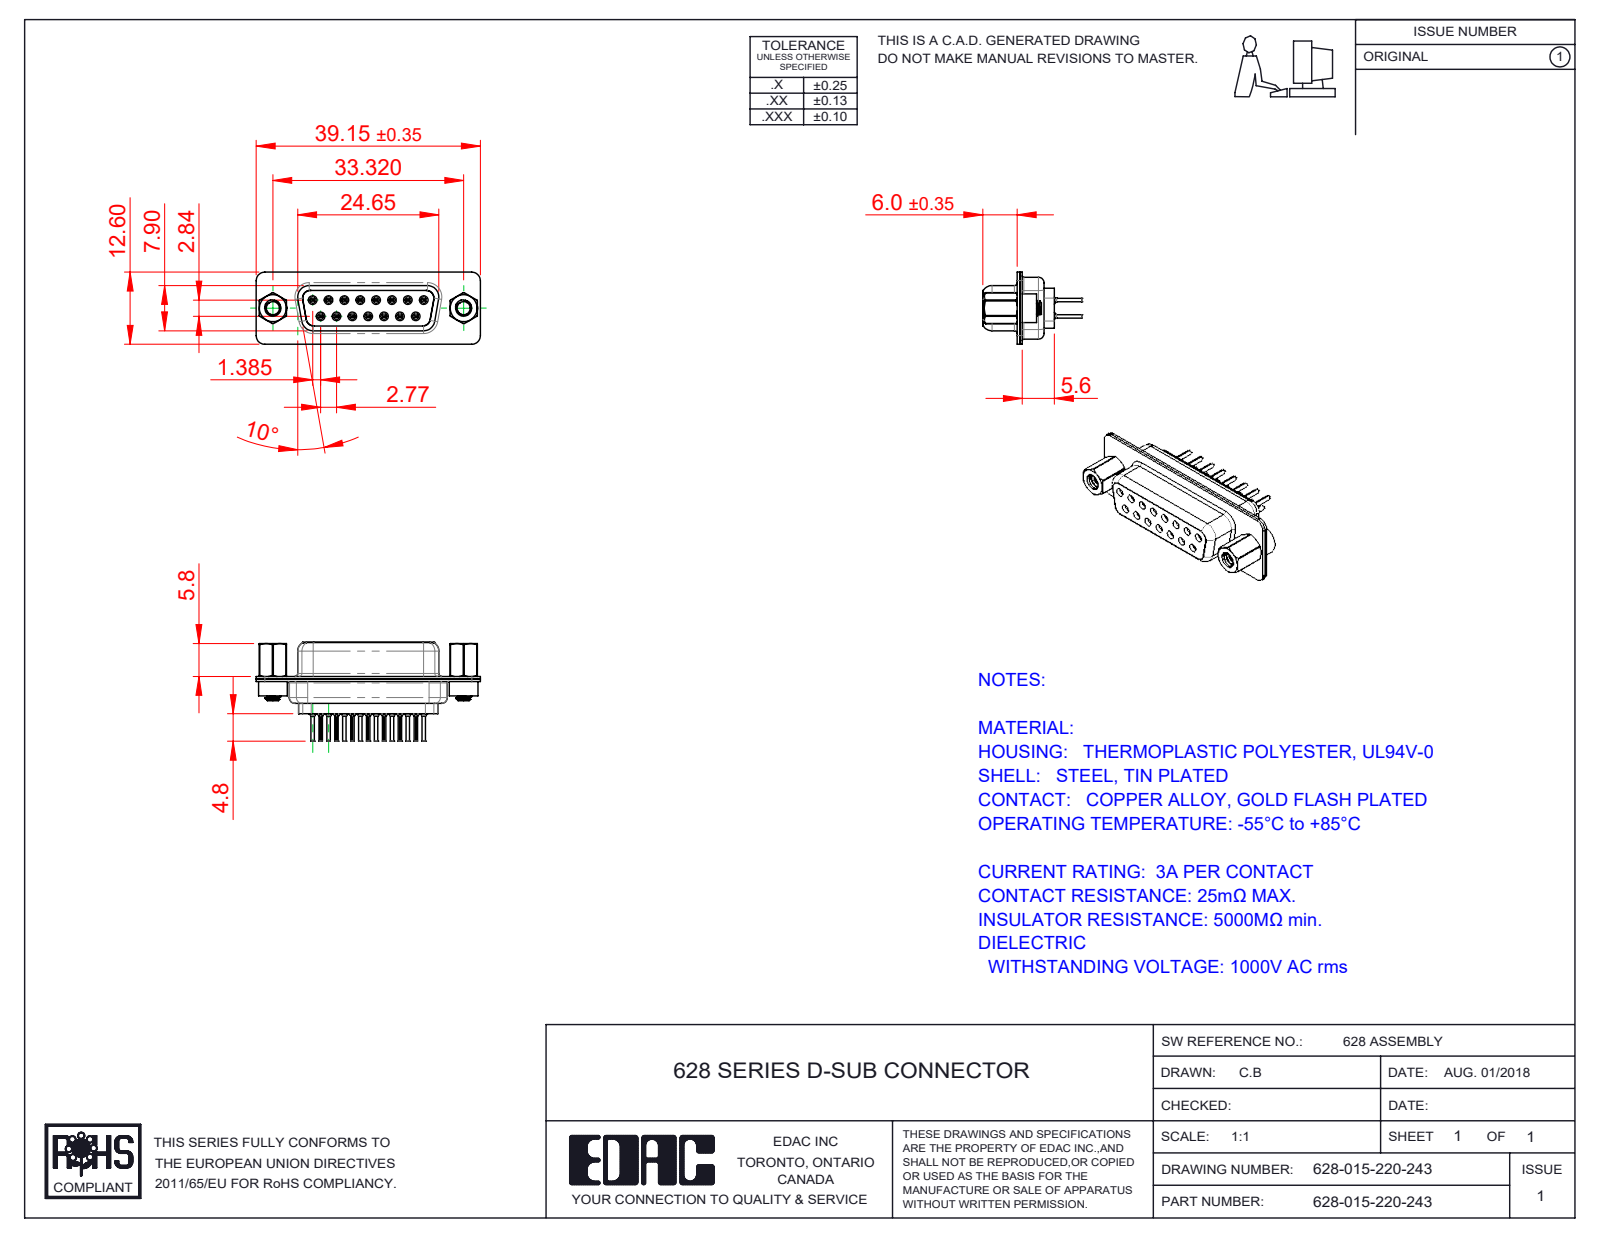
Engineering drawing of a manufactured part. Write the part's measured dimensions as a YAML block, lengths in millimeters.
part_name: "628 Contact Row 2_20L; 628 Shell Rear_15 Contacts; 628 4-40 Threaded Rivet; 628-015-220-243 (+4 more)"
step_written_by: "SolidWorks 2020 (CONFIG_CONTROL_DESIGN)"
units: millimeters
bodies: {solids: 22, faces: 2306, planar: 554, cylindrical: 702, other: 1050}
overall_size: [39.15, 17.3, 12.6]
volume: 2750
surface_area: 6798
round_holes:
  - {diameter: 0.2, count: 15}
  - {diameter: 0.8, count: 15}
  - {diameter: 0.9, count: 15}
  - {diameter: 1.1, count: 15}
  - {diameter: 1.6, count: 15}
  - {diameter: 1.7, count: 8}
  - {diameter: 2.26, count: 2}
  - {diameter: 2.29, count: 2}
  - {diameter: 4, count: 2}
  - {diameter: 4.05, count: 2}
  - {diameter: 4.85, count: 2}
round_bosses_or_shafts:
  - {diameter: 2, count: 15}
  - {diameter: 1.5, count: 15}
  - {diameter: 1.2, count: 15}
  - {diameter: 0.6, count: 15}
  - {diameter: 5, count: 2}
  - {diameter: 4.95, count: 2}
  - {diameter: 4.8, count: 2}
  - {diameter: 2.79, count: 2}
partial_cylinders:
  - {radius: 0.1, count: 30}
  - {radius: 1.5, count: 18}
  - {radius: 0.28, count: 15}
  - {radius: 2, count: 12}
  - {radius: 1.35, count: 8}
  - {radius: 0.25, count: 4}
  - {radius: 0.5, count: 4}
  - {radius: 0.6, count: 4}
face_to_face_distances: [0.45, 0.4, 0.9, 6.6, 1.9, 8.5, 1.4, 0.85, 7.05, 7.45]
hole_center_spacings: [3.16, 2.77, 5.54, 8.31, 11.08, 5.03, 5.04, 7.48]
